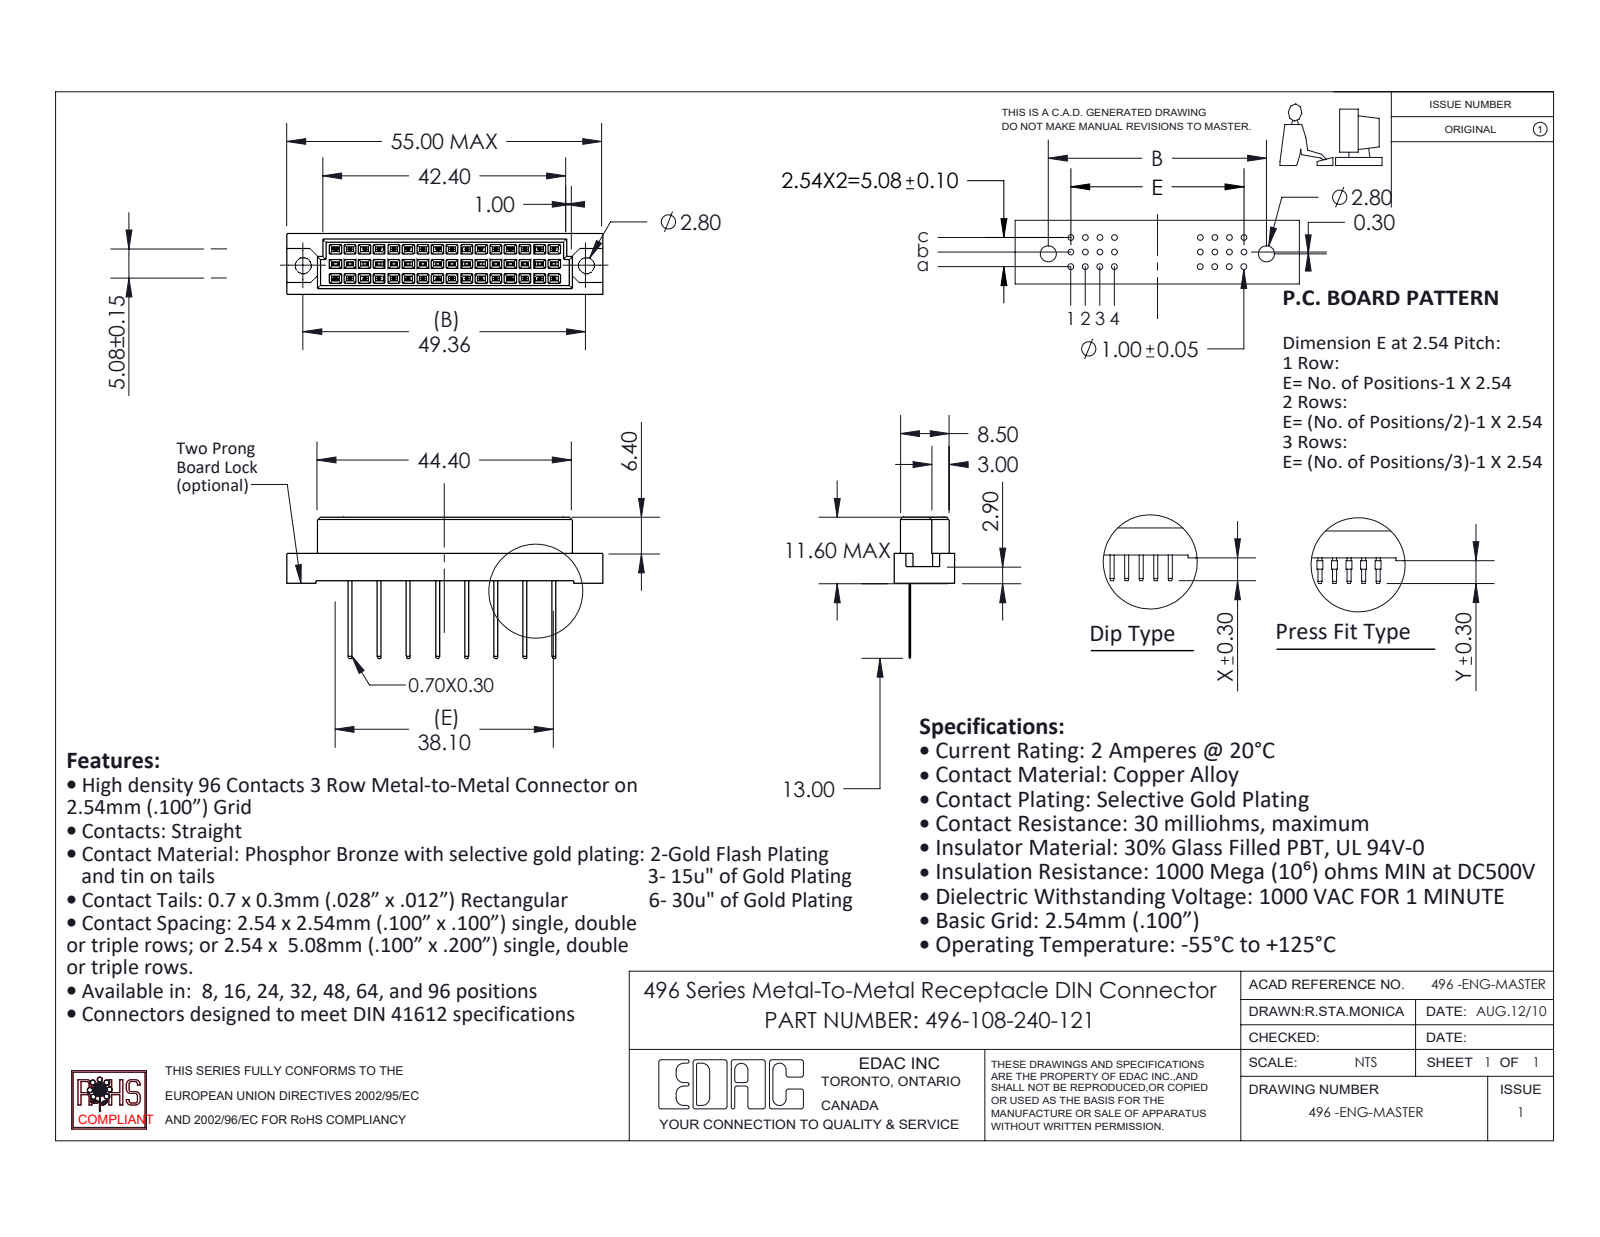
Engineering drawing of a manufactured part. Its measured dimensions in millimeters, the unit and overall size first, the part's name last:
Units: millimetres
Overall size (bounding box): 55 × 24.6 × 10.6
Round holes (diameter × count): ⌀2.8 ×2
Main face-to-face distances: 2.54, 5.08, 1.05, 9.55, 0.81, 10.6, 3.35, 1.73, 8.5, 0.56
Hole centre spacings: 49.36
Volume: 4 619 mm³ · Surface area: 4 501 mm²
Bodies: 9 solids, 746 faces (742 planar, 4 cylindrical, 0 other)
Part name (STEP PRODUCT): 496-290_40; 496 Part_48; 496-108-240-121
STEP written by: SolidWorks 2020 (CONFIG_CONTROL_DESIGN)
